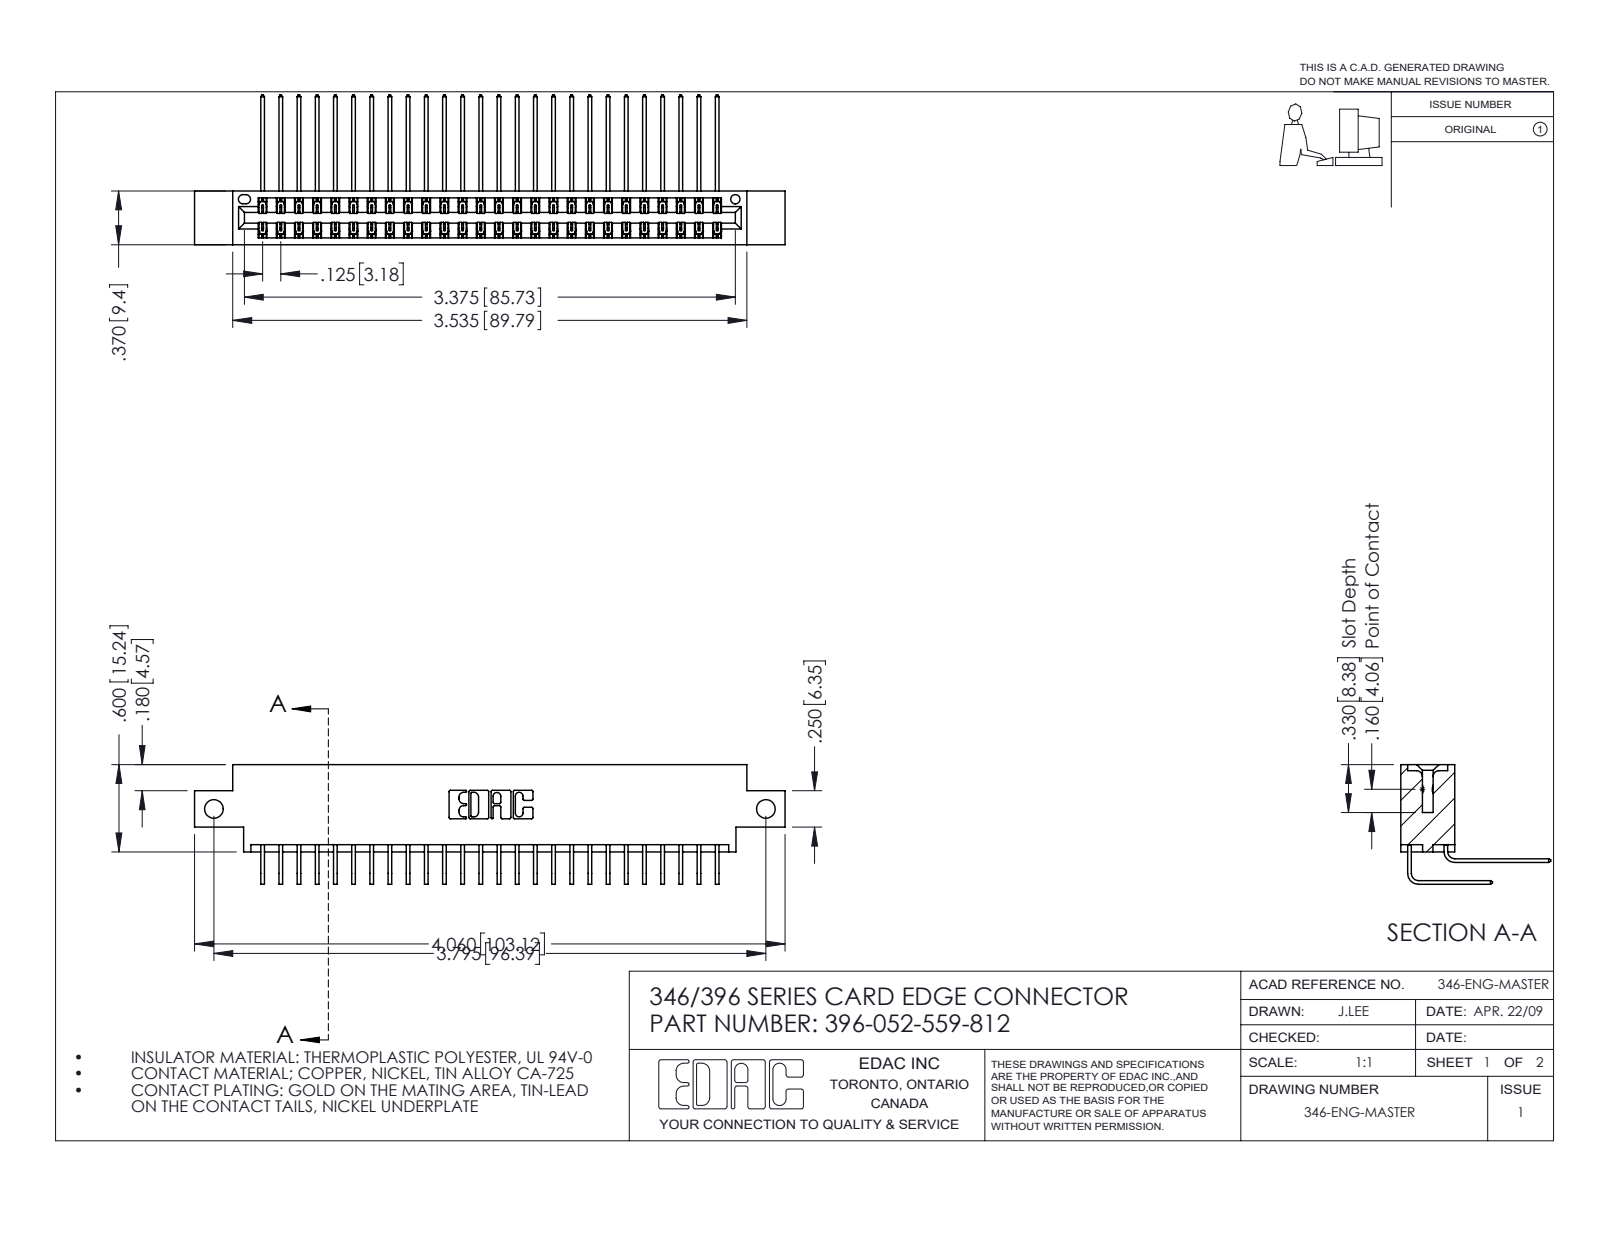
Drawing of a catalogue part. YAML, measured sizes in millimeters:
part_name: "396-052-559-812; 346 Part_0.170 Offset - Side Mount; 345-292-001_558 559 Tail - 1; 345-292-001_559 Tail - 2"
step_written_by: "SolidWorks 2016 (CONFIG_CONTROL_DESIGN)"
units: millimeters
bodies: {solids: 53, faces: 2934, planar: 2004, cylindrical: 930, other: 0}
overall_size: [103.1, 26.2, 20.9]
volume: 10000
surface_area: 14960
round_holes:
  - {diameter: 3.3, count: 2}
  - {diameter: 1.6, count: 1}
partial_cylinders:
  - {radius: 0.2, count: 78}
  - {radius: 0.3, count: 22}
  - {radius: 0.2, count: 6}
  - {radius: 0.8, count: 6}
  - {radius: 0.7, count: 3}
  - {radius: 0.4, count: 2}
  - {radius: 0.6, count: 2}
  - {radius: 0.6, count: 2}
face_to_face_distances: [1.2, 8.2, 0.6, 9.4, 6.4, 1.8, 7.6, 7, 3.8, 3.8]
hole_center_spacings: [96.4]
